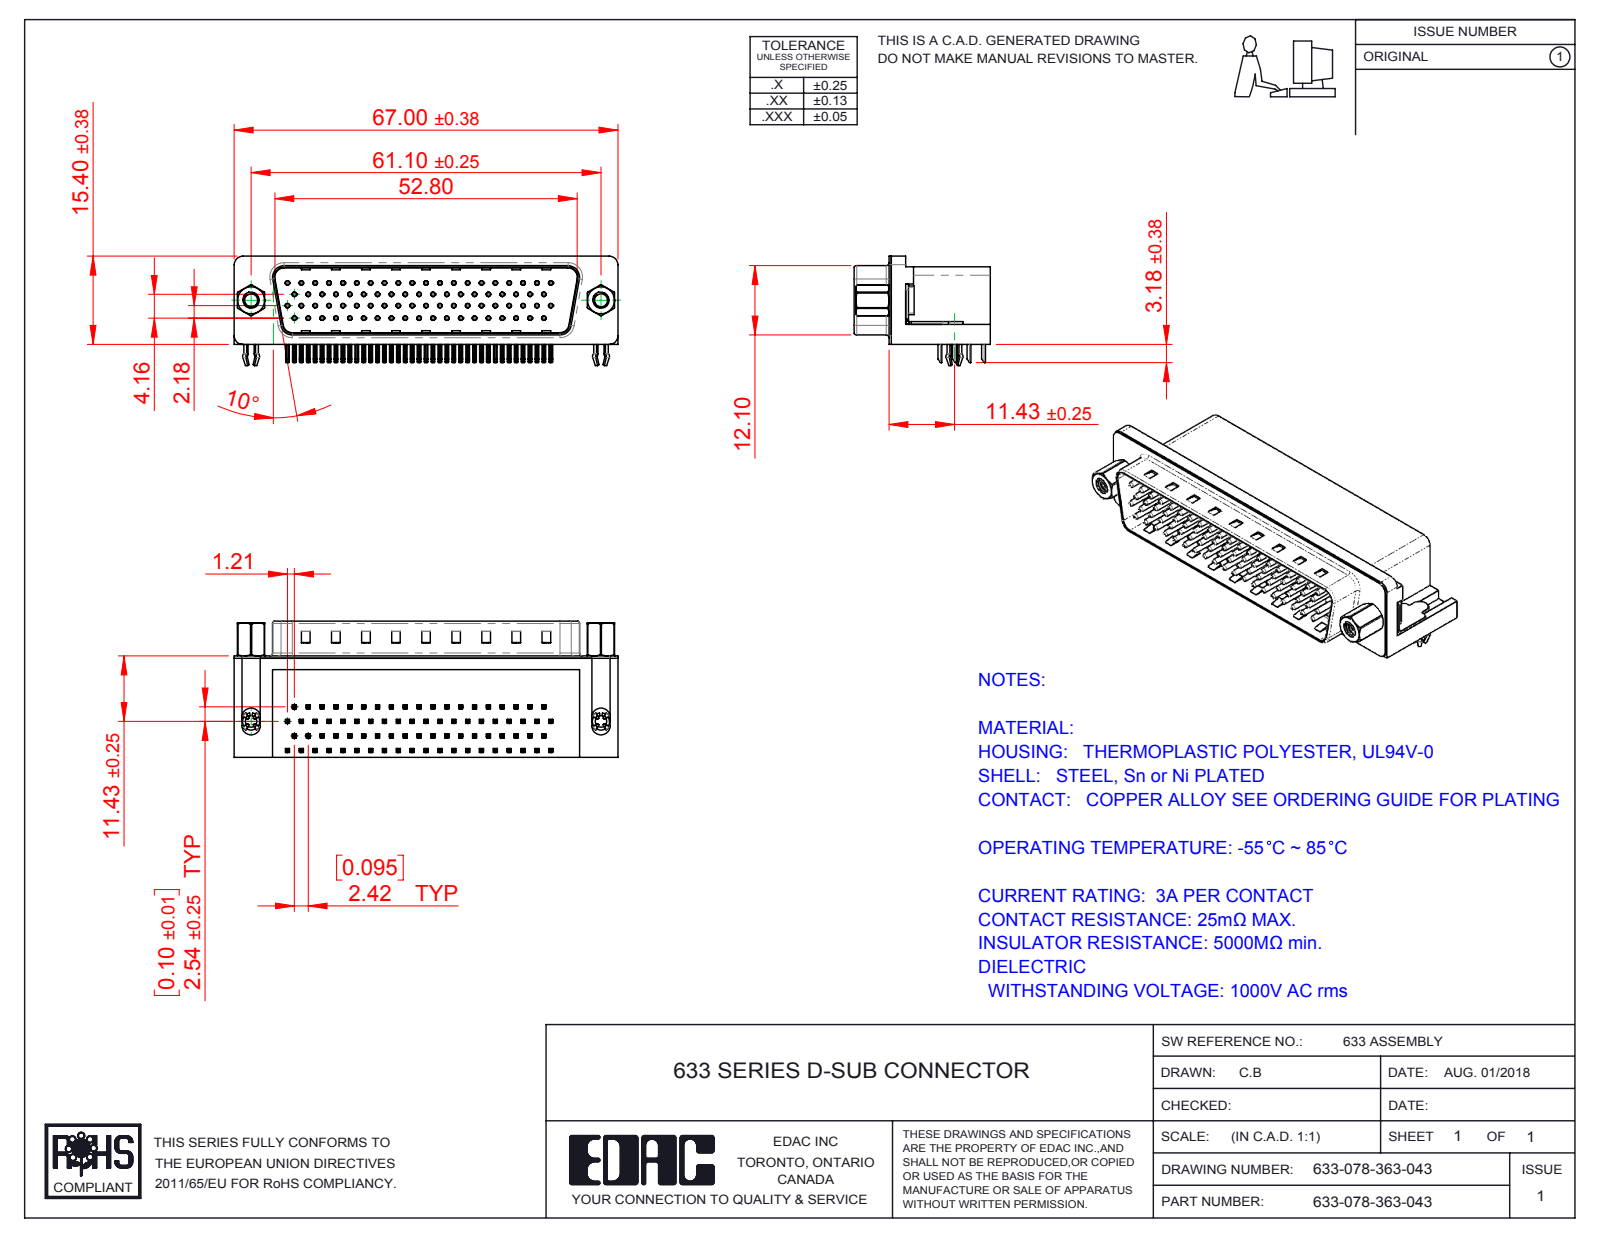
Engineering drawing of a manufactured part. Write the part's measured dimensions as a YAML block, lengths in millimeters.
part_name: "633 Contact Middle_78 Contact; 633 Contact Top_78 Contact; 633 Contact Bottom_78 Contact; 633 4-40 Hex Standoff (+6 more)"
step_written_by: "SolidWorks 2016 (CONFIG_CONTROL_DESIGN)"
units: millimeters
bodies: {solids: 86, faces: 6516, planar: 4045, cylindrical: 1848, other: 623}
overall_size: [67, 23.8, 19.1]
volume: 14825
surface_area: 16882
round_holes:
  - {diameter: 0.35, count: 78}
  - {diameter: 0.8, count: 78}
  - {diameter: 2, count: 2}
  - {diameter: 2.26, count: 2}
  - {diameter: 2.29, count: 2}
  - {diameter: 4, count: 2}
  - {diameter: 4.8, count: 2}
  - {diameter: 5, count: 2}
round_bosses_or_shafts:
  - {diameter: 0.75, count: 78}
  - {diameter: 4.9, count: 2}
  - {diameter: 4.75, count: 2}
  - {diameter: 3.9, count: 2}
  - {diameter: 3, count: 2}
  - {diameter: 2.79, count: 2}
partial_cylinders:
  - {radius: 0.25, count: 324}
  - {radius: 0.12, count: 156}
  - {radius: 1, count: 16}
  - {radius: 0.5, count: 9}
  - {radius: 1.6, count: 8}
  - {radius: 1.5, count: 6}
  - {radius: 0.45, count: 4}
  - {radius: 0.9, count: 4}
face_to_face_distances: [0.4, 13.2, 17.3, 11.7, 13.35, 2.05, 13.75, 1.65, 1.85, 11.9]
hole_center_spacings: [2.42, 4.84, 7.26, 9.68, 6.26, 7.13, 12.1, 8.62]
